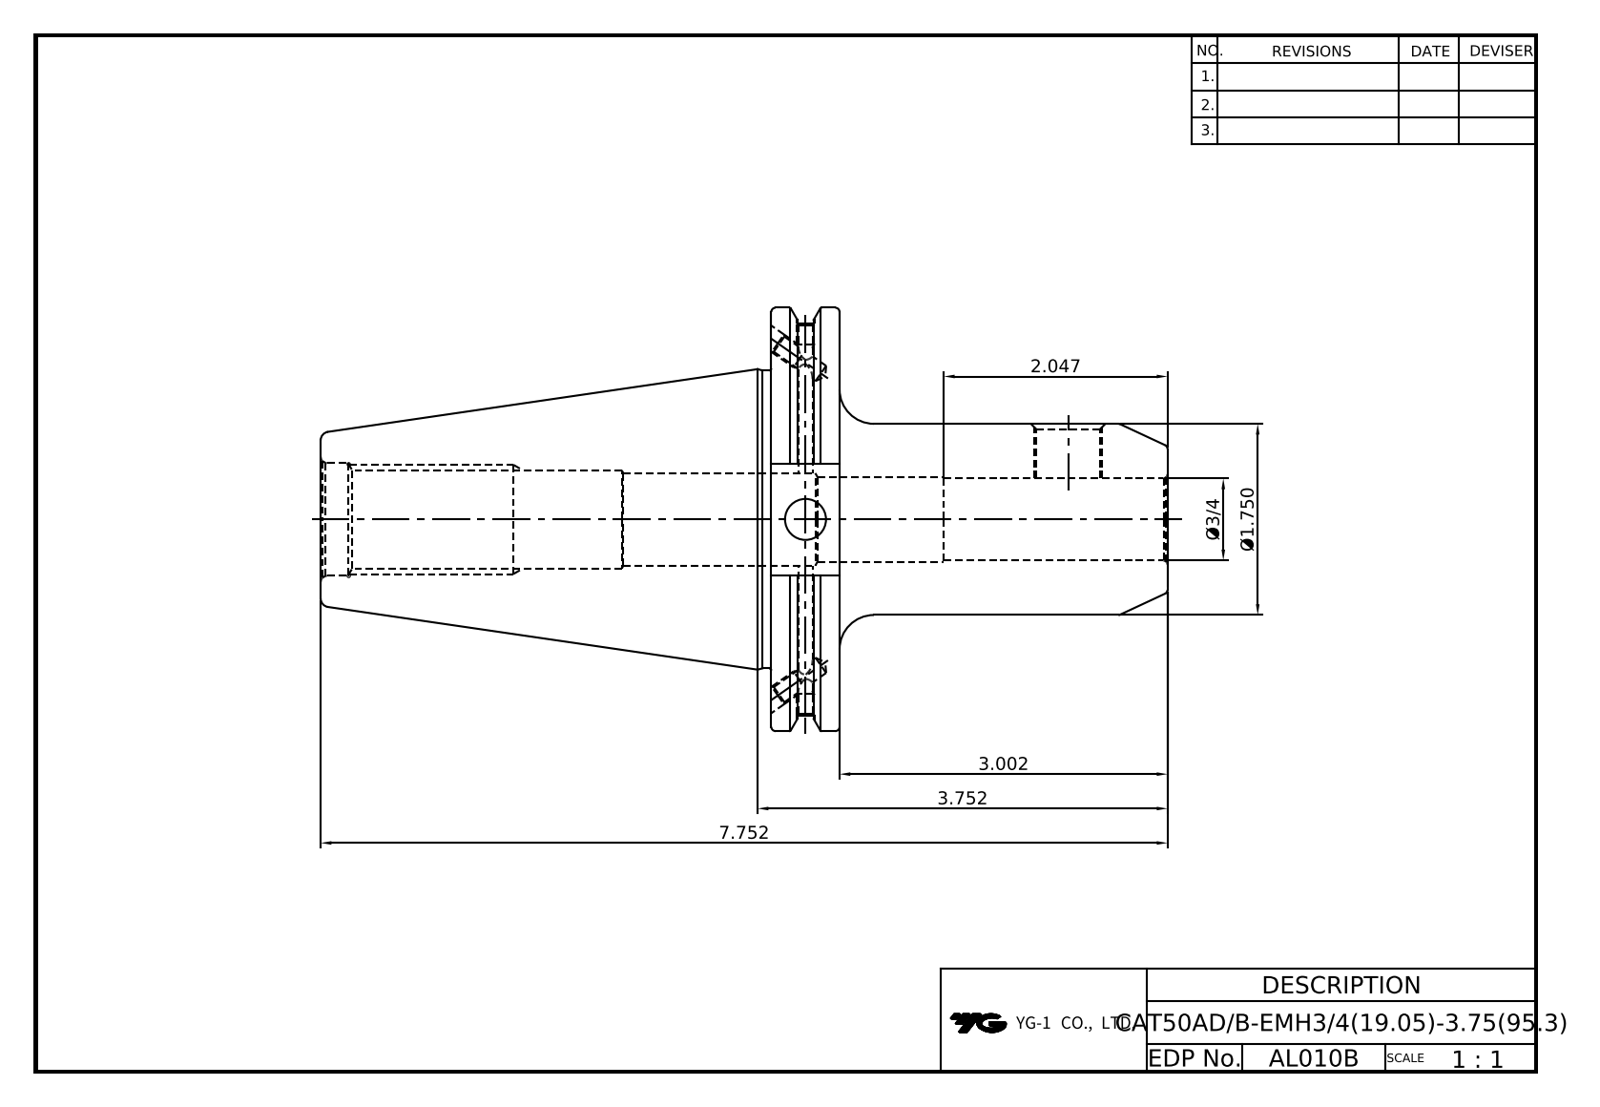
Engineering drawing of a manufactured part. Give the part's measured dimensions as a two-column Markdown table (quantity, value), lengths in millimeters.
| quantity | value |
| --- | --- |
| part name | LO-CAT50ADB-EMH19.05-95.3 |
| STEP written by | Autodesk Inventor 2020 (AUTOMOTIVE_DESIGN) |
| units | millimeters |
| bodies | 1 solid, 88 faces (37 planar, 27 cylindrical, 24 other) |
| overall size | 196.9 × 98.42 × 94.69 |
| volume | 409 630 mm³ |
| surface area | 59 578 mm² |
| round holes (diameter × count) | 3.24 × 2, 4.13 × 2, 4.2 × 2, 5 × 2, 9.53 × 1, 14.35 × 1, 19.05 × 1, 19.65 × 1, 21.5 × 1, 21.97 × 1, 26.2 × 1 |
| round bosses / shafts (diameter × count) | 98.42 × 1, 91.29 × 1, 69.25 × 1, 44.45 × 1 |
| main face-to-face distances | 15.88, 92.13, 76.25, 104.77, 120.65, 196.9, 73.03, 25.9, 110.82, 6.05 |
